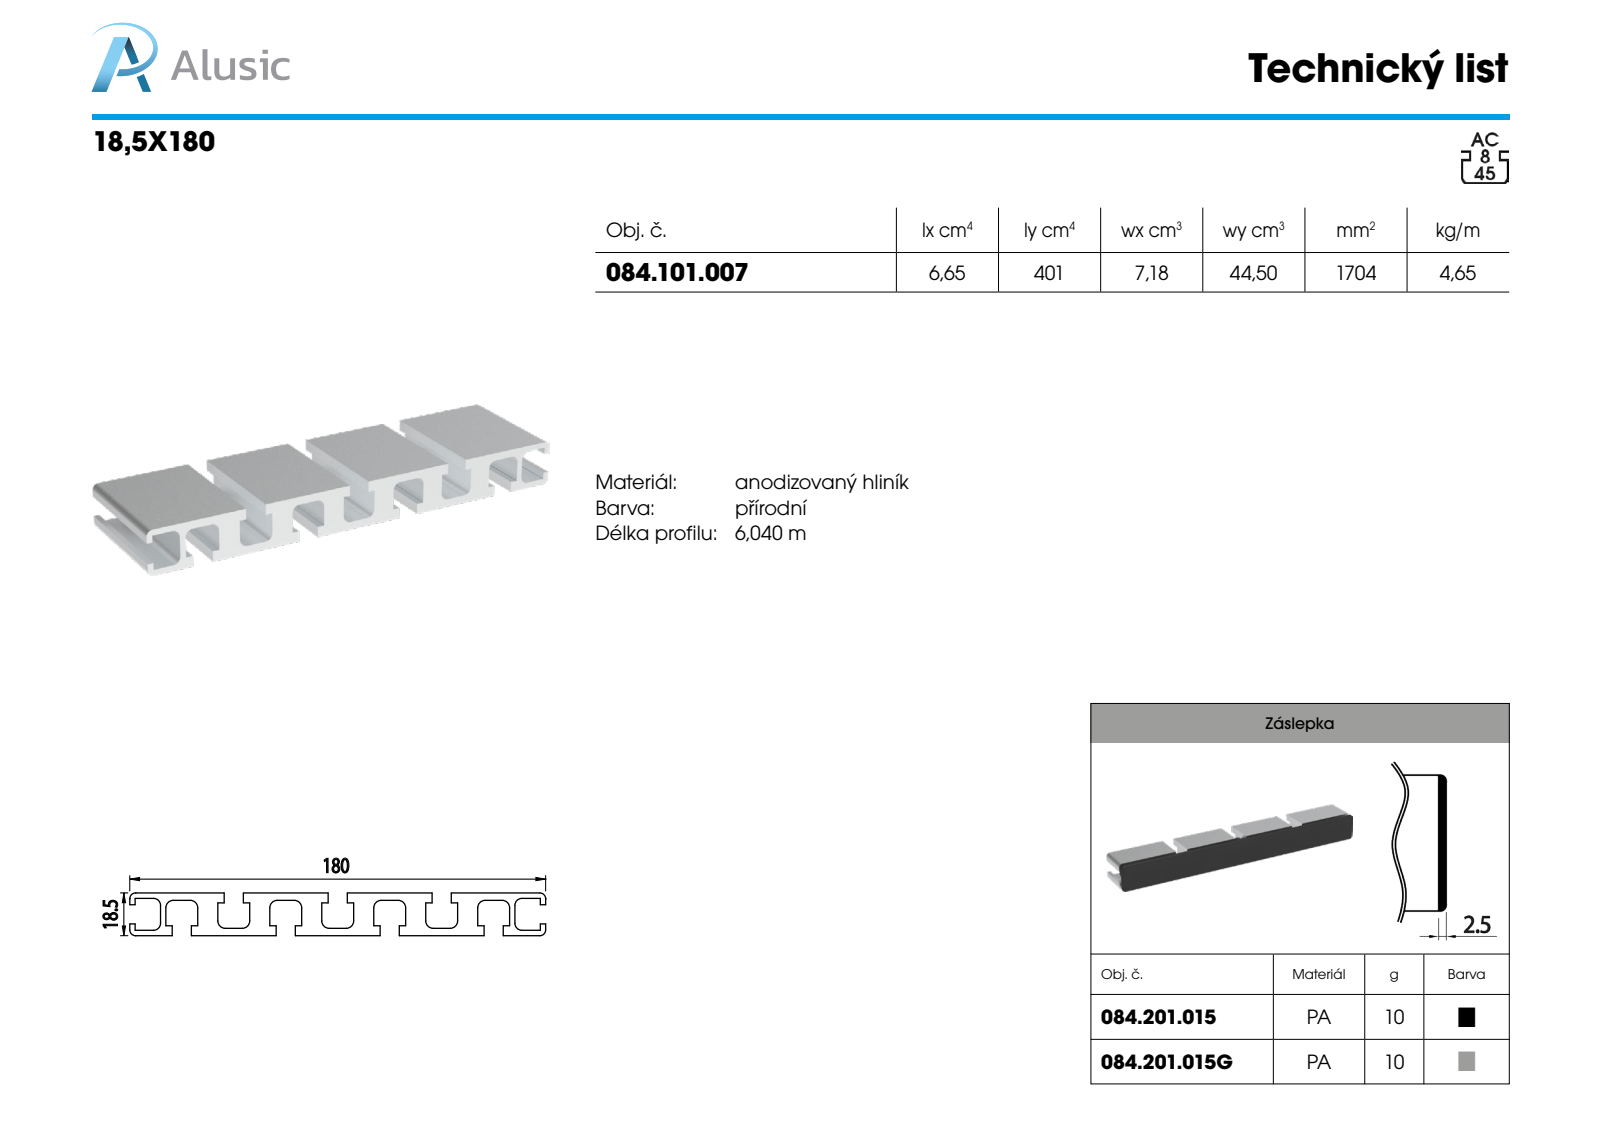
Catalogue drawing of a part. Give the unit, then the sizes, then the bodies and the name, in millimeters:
Units: millimetres
Overall size (bounding box): 180 × 18.5 × 12
Round holes (diameter × count): ⌀9.5 ×3
Round bosses / shafts (diameter × count): ⌀13 ×3
Partial cylindrical surfaces — rounded edges, fillets, slot ends (radius × count): R2 ×4, R2.5 ×4
Main face-to-face distances: 2.5, 12, 9.5, 18.5, 180
Hole centre spacings: 80.5, 161
Volume: 9 733 mm³ · Surface area: 9 280 mm²
Bodies: 1 solid, 42 faces (12 planar, 20 cylindrical, 10 other)
Part name (STEP PRODUCT): 084.201.015
STEP written by: SolidWorks 2011 (CONFIG_CONTROL_DESIGN)
